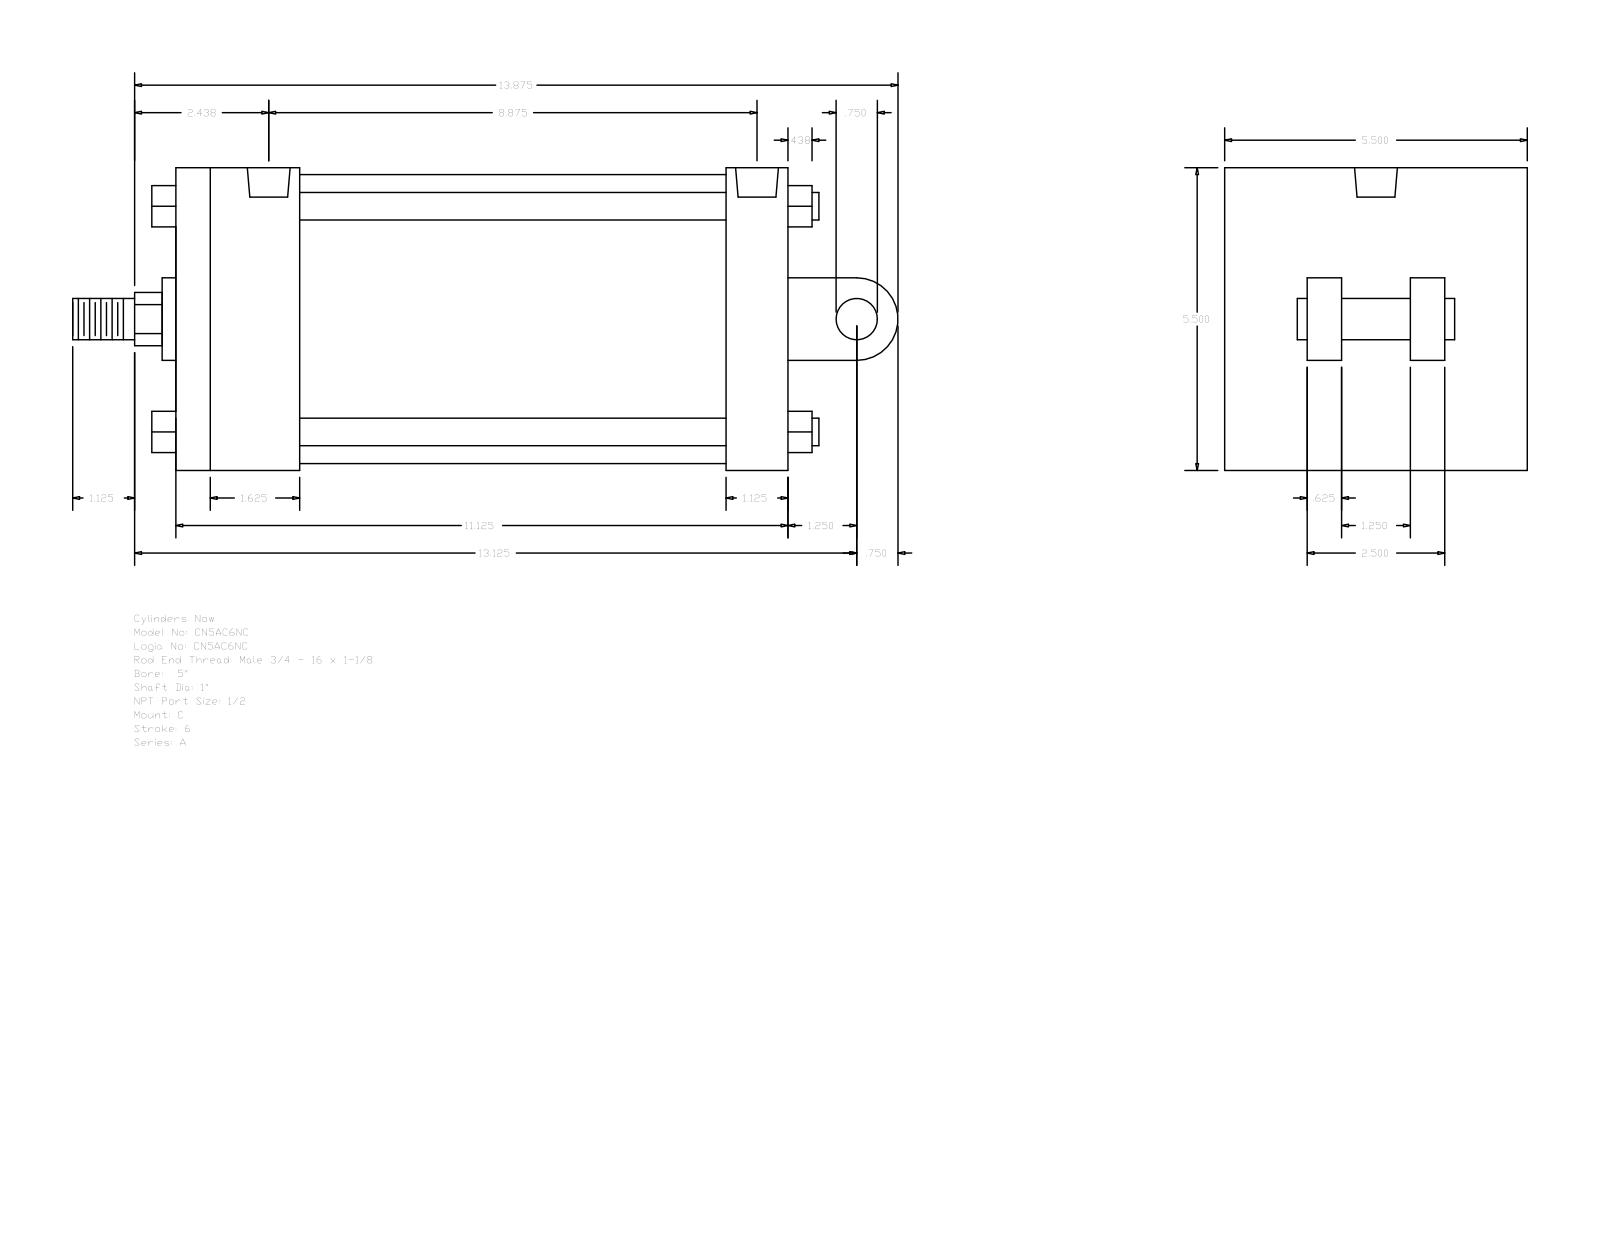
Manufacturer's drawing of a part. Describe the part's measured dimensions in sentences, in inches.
The part is named "A_C__0500_1". Its 3-D file was written by "GSSL Pune (CONFIG_CONTROL_DESIGN)". It is 0 solids with 135 faces: 102 planar, 33 cylindrical and 0 other. Overall it measures 15 by 5.5 by 5.5 inches. Round holes: 4 of diameter 0.344, 2 of diameter 0.778. Round bosses or shafts: 4 of diameter 0.5, 2 of diameter 0.75, 1 of diameter 5.25, 1 of diameter 1.5, 1 of diameter 1. Partial cylindrical surfaces (rounded edges, fillets, slot ends): 1 of radius 0.484, 1 of radius 0.75. The main face-to-face distances are 5.5, 11.125, 1.125, 2.25, 10, 7.75, 8.875, 1.5, 4, 2.125. The hole center spacings are 0.094, 8.687, 8.781, 8.875.
